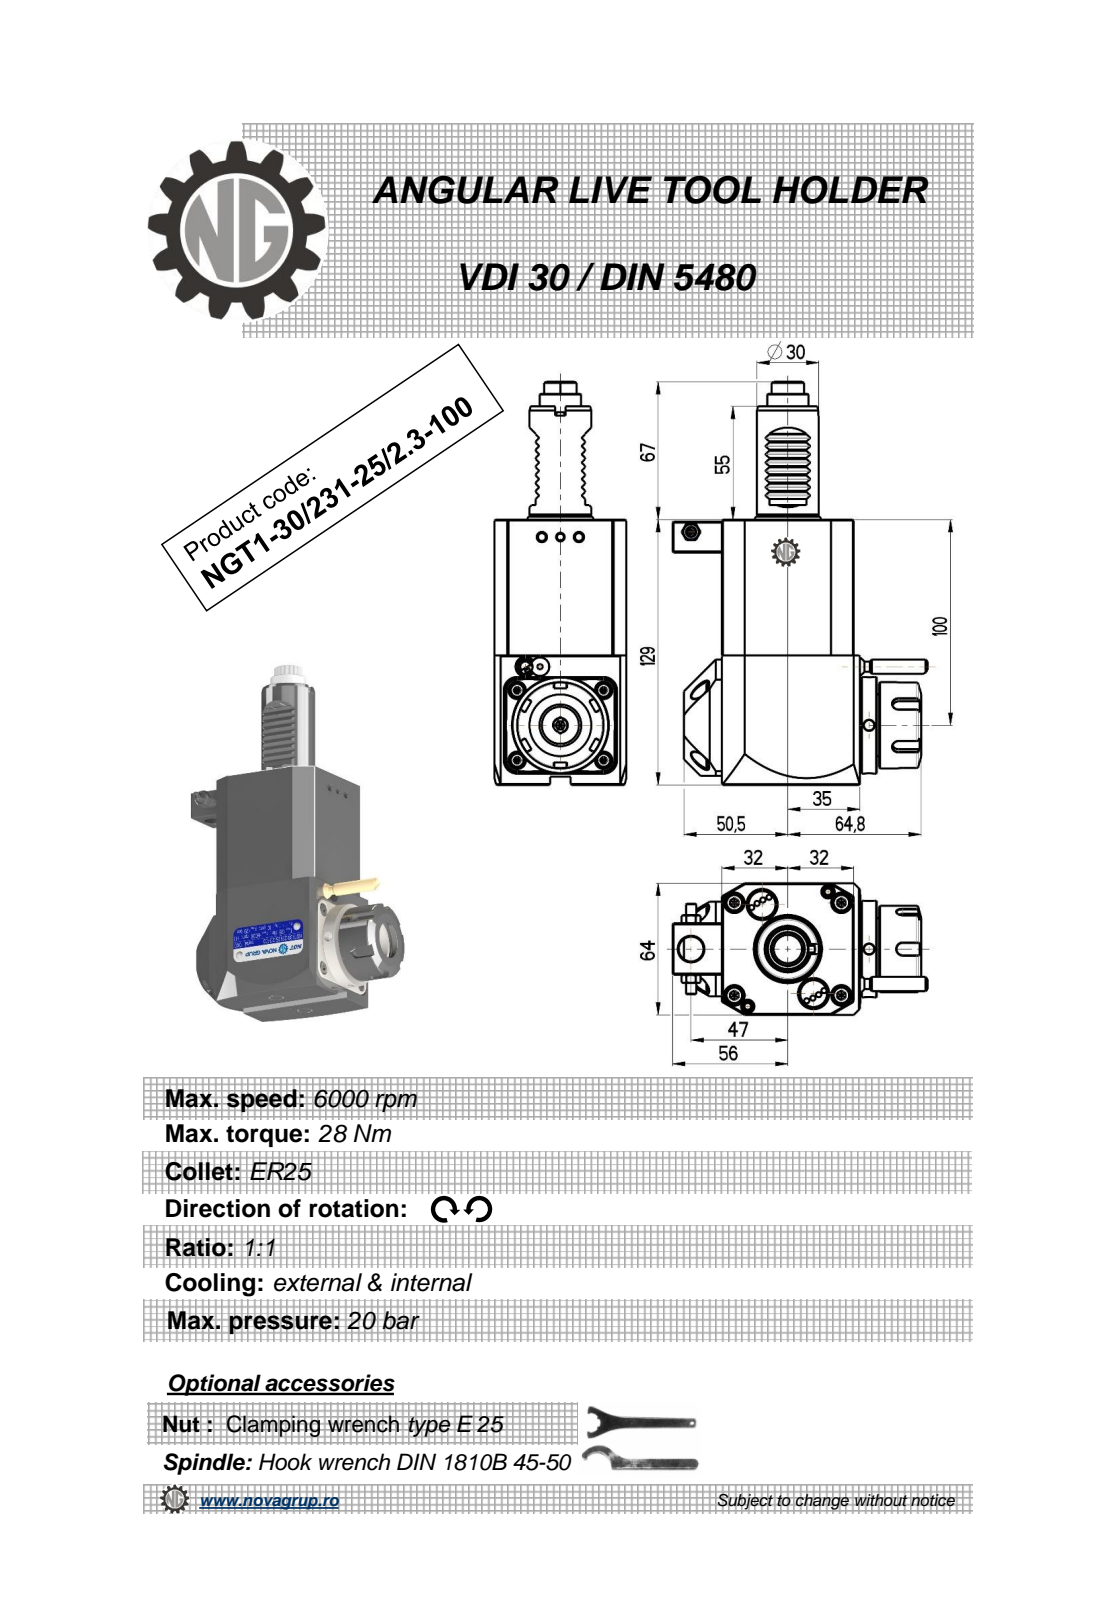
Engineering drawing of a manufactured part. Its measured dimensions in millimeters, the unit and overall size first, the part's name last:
Units: millimetres
Overall size (bounding box): 196 × 123.83 × 64
Round holes (diameter × count): ⌀5 ×2, ⌀2.5 ×1, ⌀3 ×1, ⌀4.2 ×1, ⌀9.5 ×1, ⌀12 ×1, ⌀20.3 ×1
Round bosses / shafts (diameter × count): ⌀8.96 ×2, ⌀5 ×2, ⌀47 ×1, ⌀42 ×1, ⌀35 ×1, ⌀30 ×1, ⌀20 ×1, ⌀7 ×1
Partial cylindrical surfaces — rounded edges, fillets, slot ends (radius × count): R1.98 ×36, R0.3 ×16, R0.26 ×12, R3 ×5, R160 ×2, R7.08 ×1, R7.92 ×1, R13 ×1
Main face-to-face distances: 64, 129, 76.42, 0.5, 67.2, 3.2, 67, 7.5, 3, 2.83
Hole centre spacings: 33.19, 65.25, 86.45, 91.5, 127.71
Volume: 641 688 mm³ · Surface area: 59 274 mm²
Bodies: 1 solid, 550 faces (223 planar, 161 cylindrical, 166 other)
Part name (STEP PRODUCT): NGT1_30_231_25_2_3_100
STEP written by: PRO/ENGINEER BY PARAMETRIC TECHNOLOGY CORPORATION, 2010280 (CONFIG_CONTROL_DESIGN)
